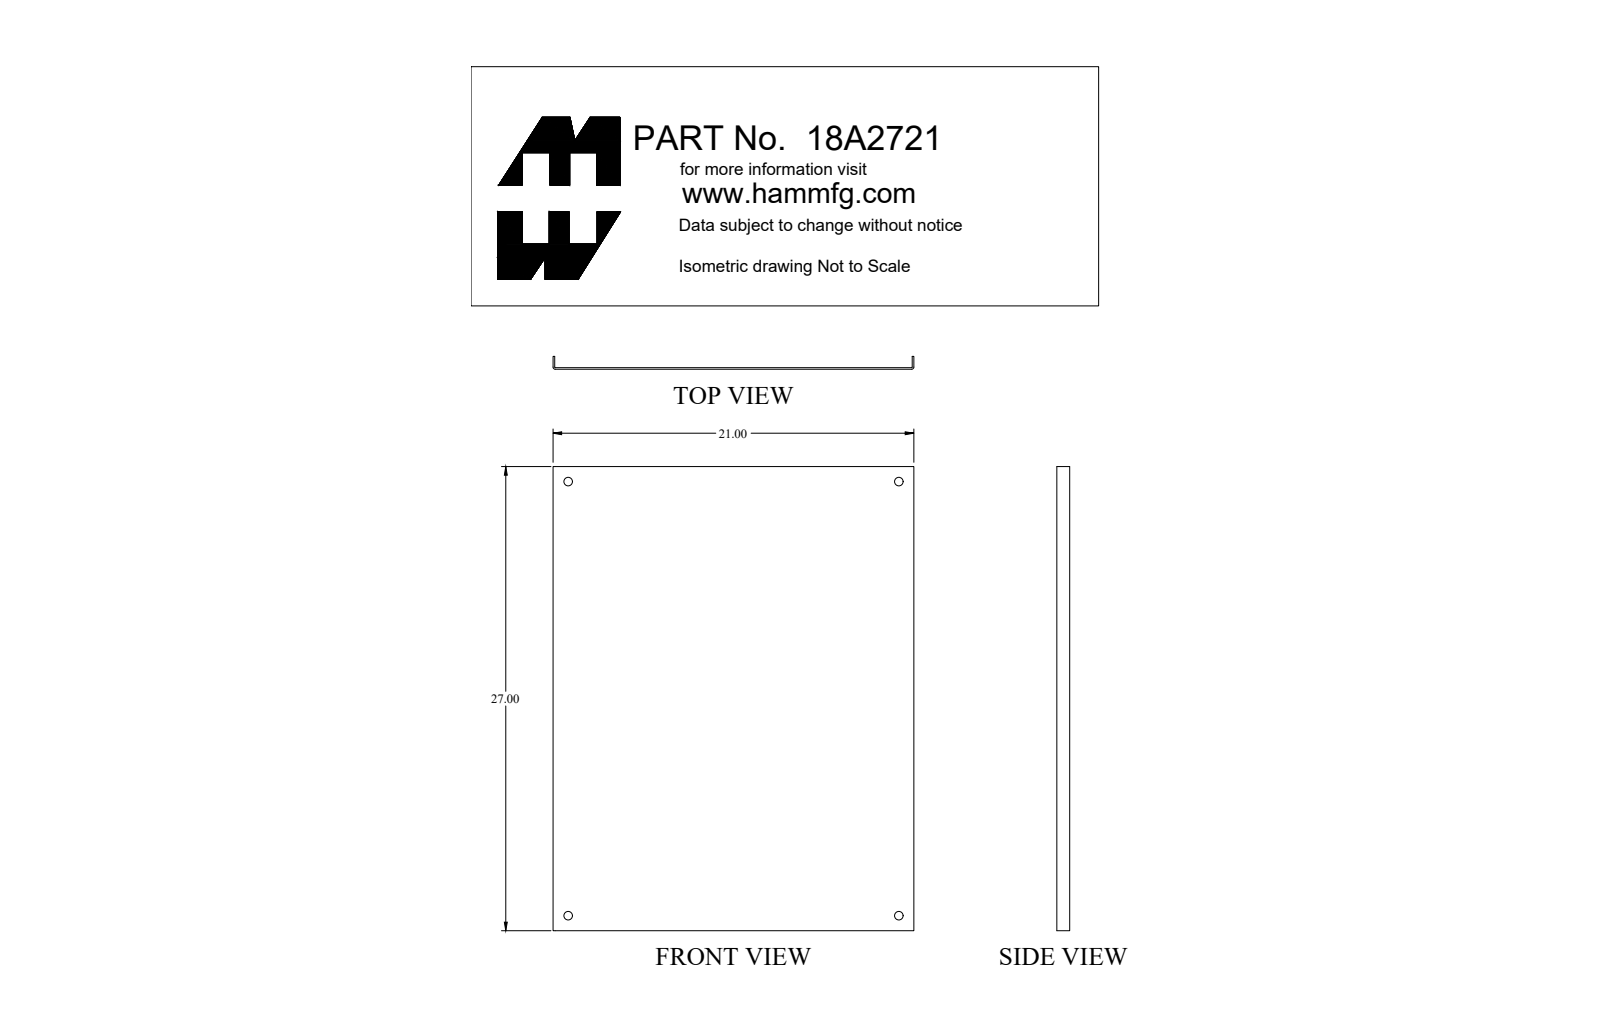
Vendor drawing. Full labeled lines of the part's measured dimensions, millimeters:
Part name (STEP PRODUCT): 18A2721
STEP written by: SolidWorks 2018 (AUTOMOTIVE_DESIGN)
Units: millimetres
Bodies: 1 solid, 18 faces (10 planar, 8 cylindrical, 0 other)
Overall size (bounding box): 685.8 × 533.4 × 19.1
Volume: 933 700 mm³ · Surface area: 780 600 mm²
Round holes (diameter × count): ⌀12.7 ×4
Partial cylindrical surfaces — rounded edges, fillets, slot ends (radius × count): R0.8 ×2, R3.2 ×2
Main face-to-face distances: 2.4, 531, 533.4, 528.6, 19.1, 16.6, 685.8
Hole centre spacings: 489, 641.4, 806.5
